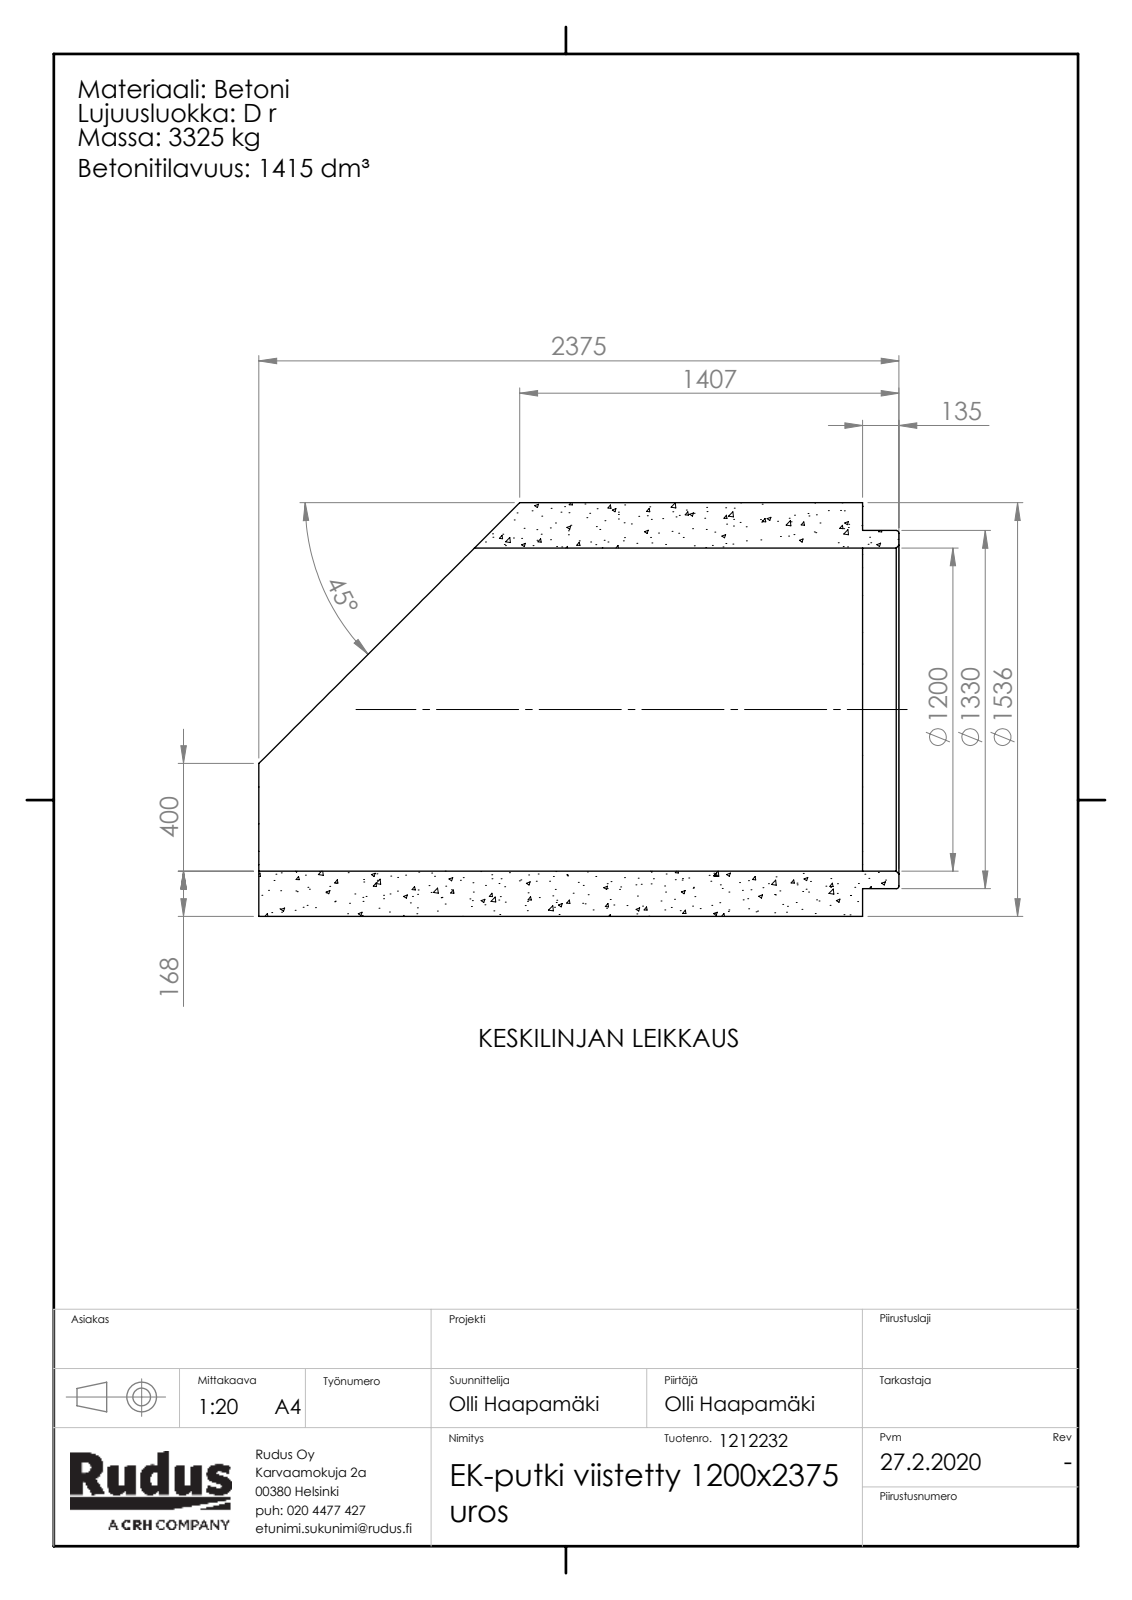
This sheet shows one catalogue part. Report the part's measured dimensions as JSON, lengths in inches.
{"part_name": "EK-osa-putkirunko_viistetty-uros; Rudus 1212232 EK-putki viistetty 1200x2375 uros", "step_written_by": "SolidWorks 2019 (CONFIG_CONTROL_DESIGN)", "units": "inches", "bodies": {"solids": 1, "faces": 93, "planar": 5, "cylindrical": 4, "other": 84}, "overall_size": [93.504, 60.472, 60.472], "volume_in3": 86350, "surface_area_in2": 29560, "round_holes": [[47.244, 1]], "round_bosses_or_shafts": [[52.362, 1]], "face_to_face_distances": [88.189, 93.504, 5.315, 47.6, 40.589, 45.904]}
